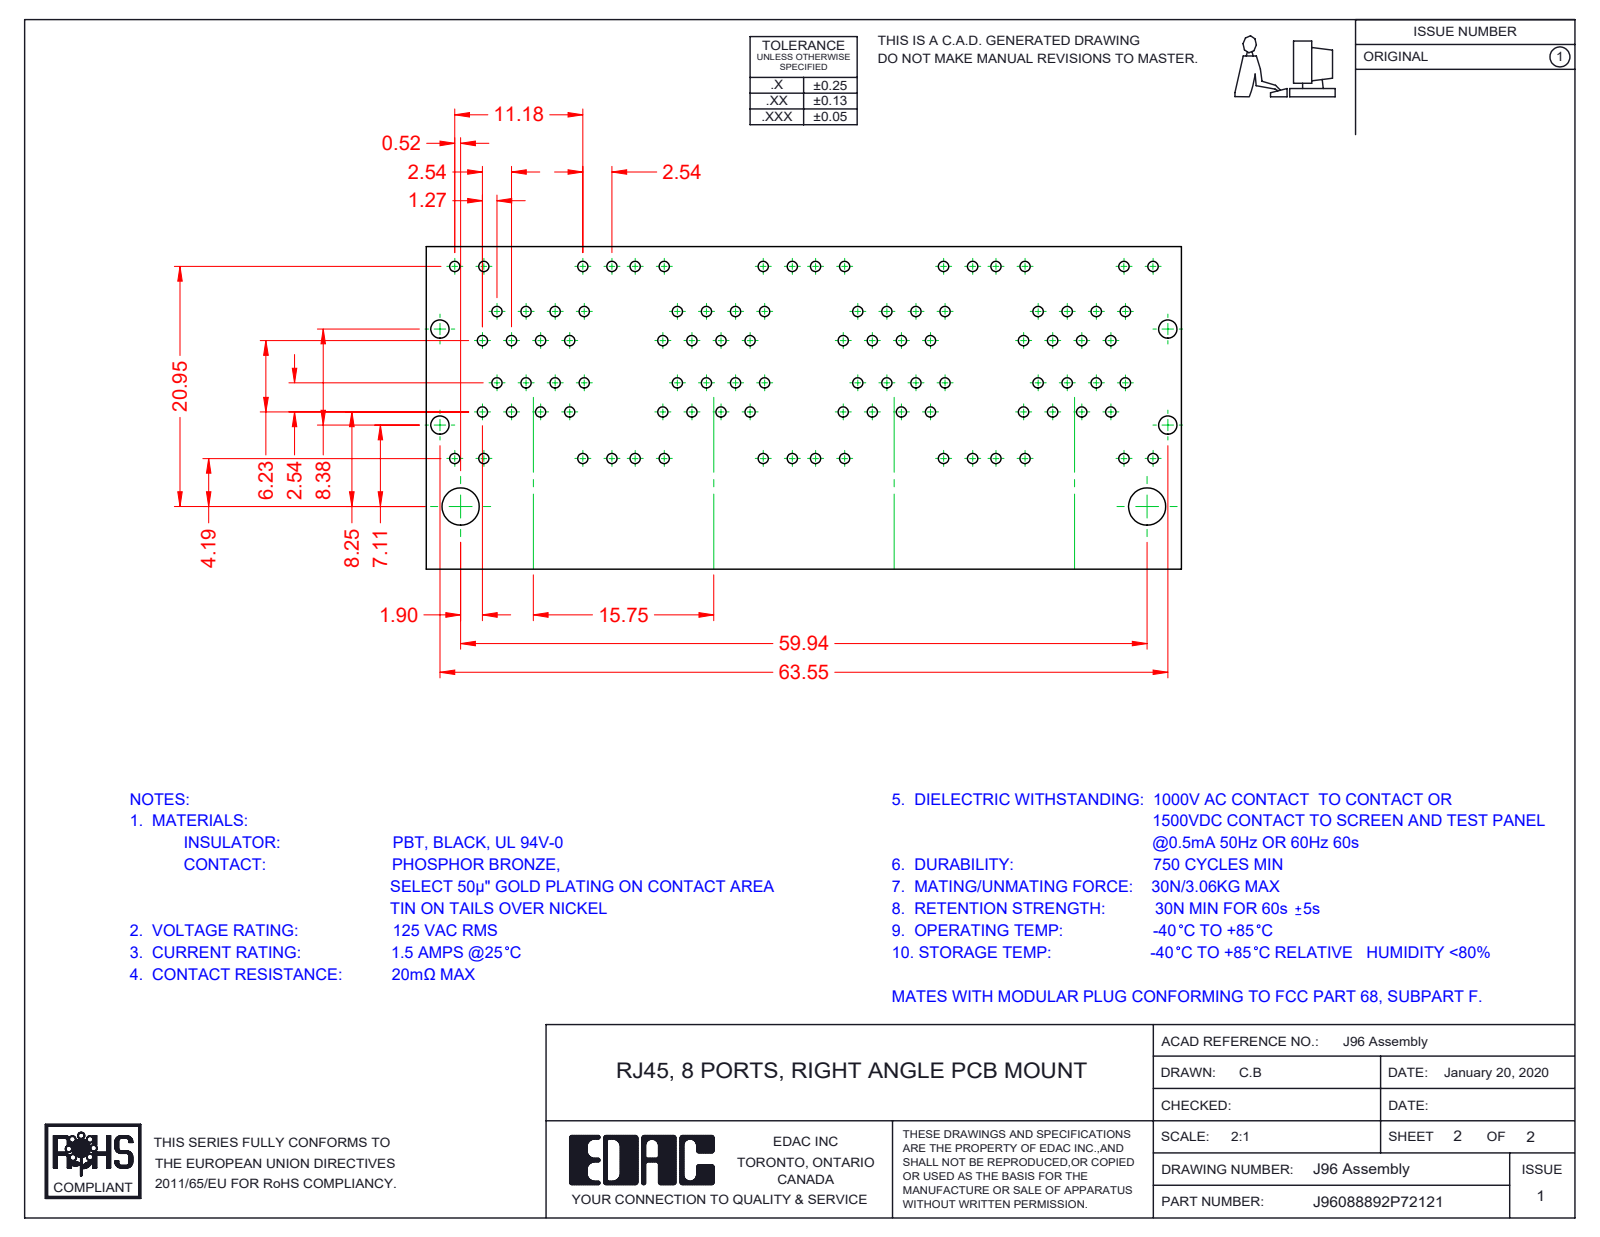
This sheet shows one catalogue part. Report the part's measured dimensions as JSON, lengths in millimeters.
{"part_name": "96 Contacts Lower; 96 Shield_8 Ports LED - No EMI; 96 Insulator Insert; 96 Contact Lock Upper (+8 more)", "step_written_by": "SolidWorks 2016 (CONFIG_CONTROL_DESIGN)", "units": "millimeters", "bodies": {"solids": 96, "faces": 7658, "planar": 6069, "cylindrical": 1323, "other": 266}, "overall_size": [64.05, 29.58, 28.68], "volume_mm3": 24160, "surface_area_mm2": 63658, "round_holes": [[1.7, 3]], "round_bosses_or_shafts": [[1.68, 3]], "partial_cylinders_radius": [[0.25, 124], [0.35, 73], [1, 72], [0.5, 49], [0.91, 32], [0.2, 21], [0.7, 11], [0.22, 8]], "face_to_face_distances": [15.75, 0.35, 9.95, 1.17, 1.6, 0.54, 9.98, 10.18, 12.67, 3.37], "hole_center_spacings": [15.75, 31.5]}
